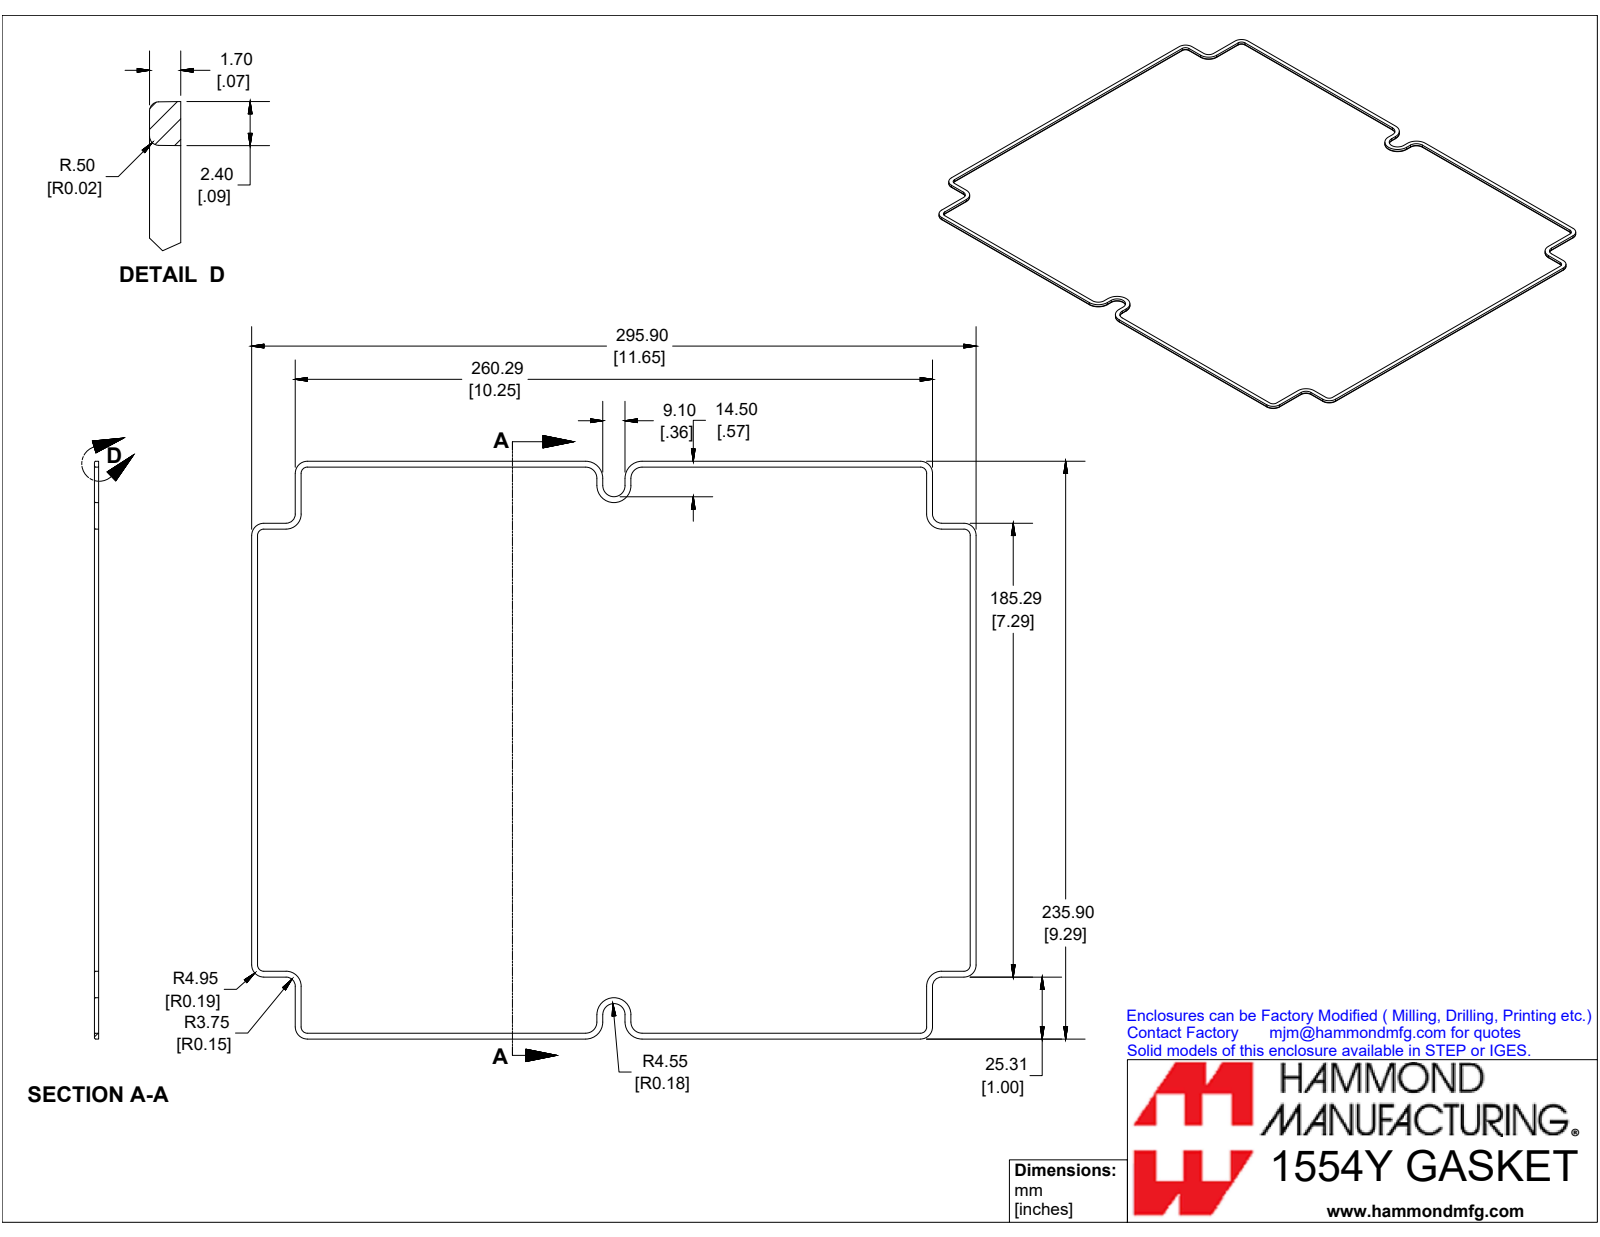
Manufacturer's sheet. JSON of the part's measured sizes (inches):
{"part_name": "1554YGASKET", "step_written_by": "SolidWorks 2019 (CONFIG_CONTROL_DESIGN)", "units": "inches", "bodies": {"solids": 1, "faces": 146, "planar": 38, "cylindrical": 36, "other": 72}, "overall_size": [11.65, 9.287, 0.067], "volume_in3": 0.257, "surface_area_in2": 12.85, "partial_cylinders_radius": [[0.02, 20]], "face_to_face_distances": [0.067, 9.193, 11.555, 0.701, 10.854, 10.154, 0.996, 8.197, 8.196, 0.996]}
